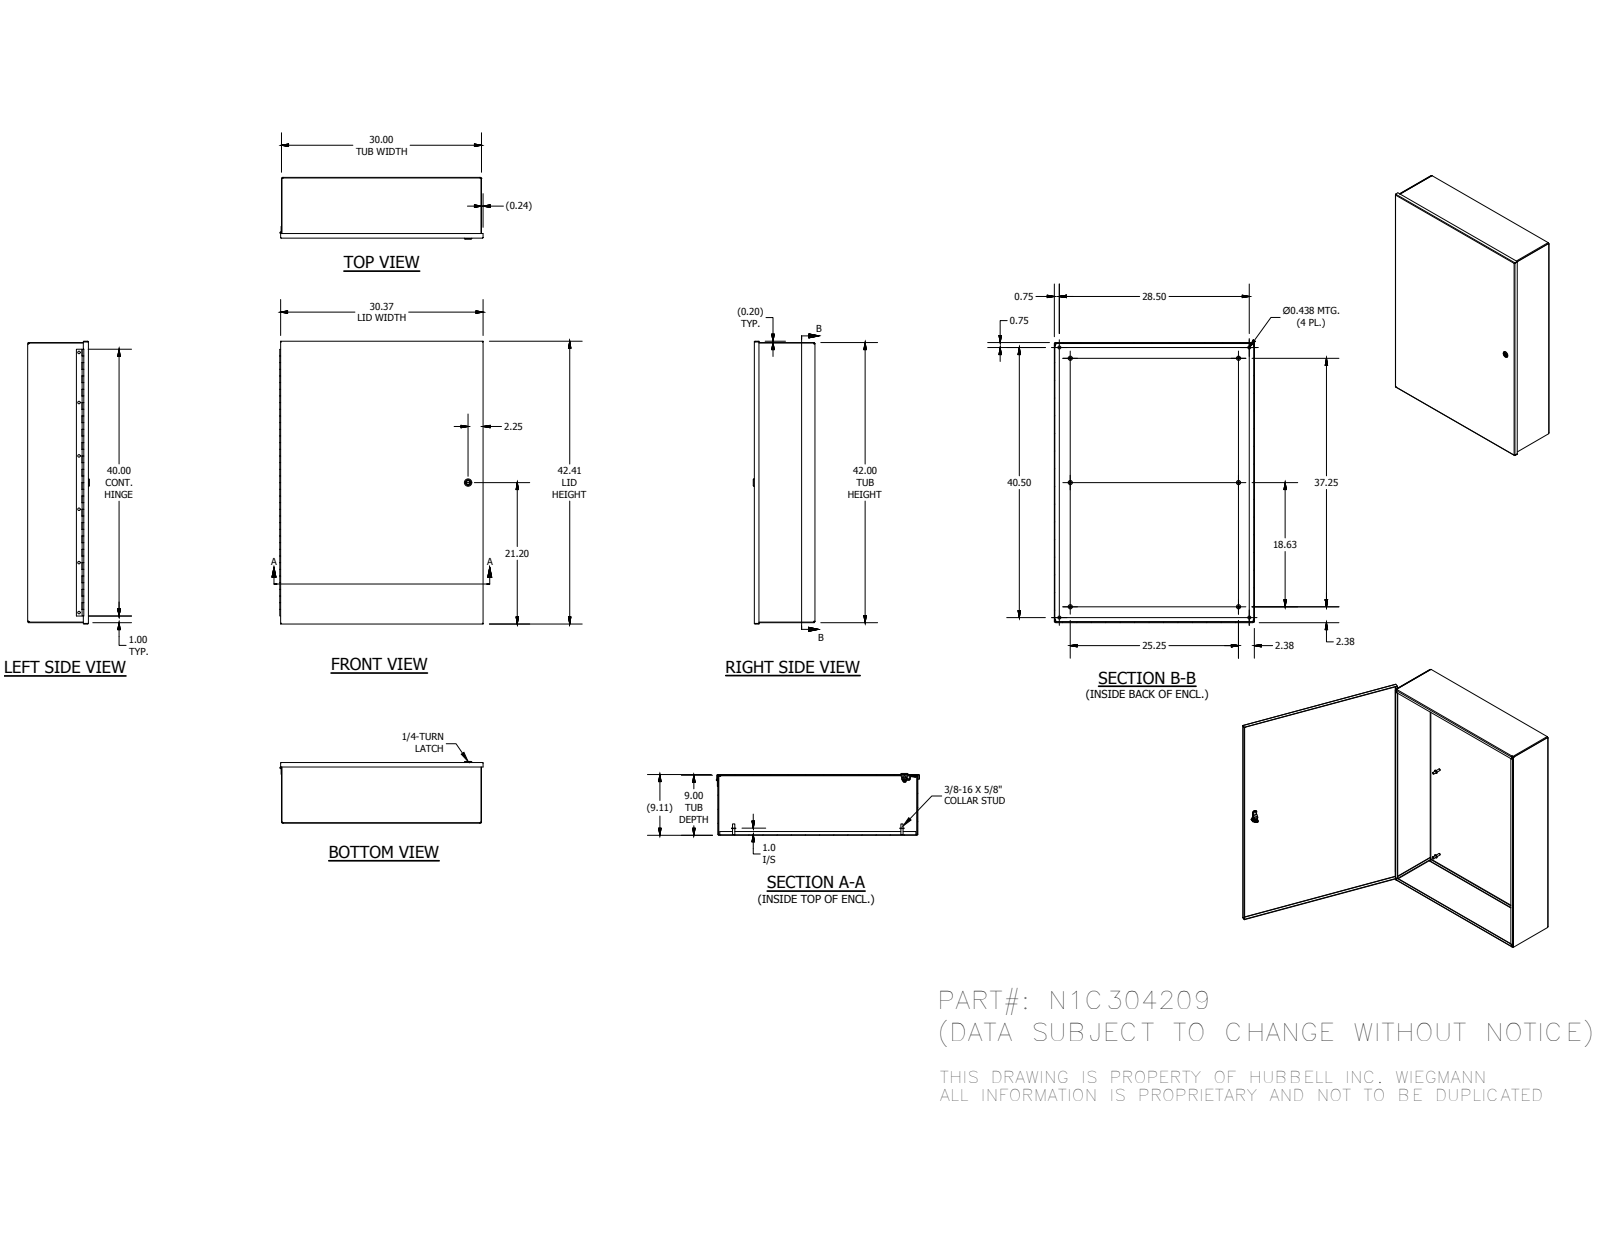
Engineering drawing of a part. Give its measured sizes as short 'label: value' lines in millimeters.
name: N1C304209BLR; N1C3009TB; N1C3042LID; 1000-101-GPF_GPD (+8 more)
written by: Autodesk Inventor 2016 (AUTOMOTIVE_DESIGN)
unit: mm
bodies: 20 solids, 978 faces (637 planar, 273 cylindrical, 68 other)
size: 1077.12 × 774.41 × 235.27
volume: 4 974 000 mm³; area: 5 333 000 mm²
holes: 6× ⌀9.52, 4× ⌀11.11, 1× ⌀3.17, 1× ⌀5, 1× ⌀8, 1× ⌀10, 1× ⌀10.2, 1× ⌀16.1, 1× ⌀20.38
bosses: 6× ⌀15.88, 6× ⌀8.38, 1× ⌀28, 1× ⌀27, 1× ⌀23, 1× ⌀19.8, 1× ⌀15.8, 1× ⌀15.2
rounds: 30× R0.3, 12× R3.47, 10× R0.5, 10× R1.59, 4× R0.79, 4× R2.67, 4× R4, 3× R0.4
face distances: 1.88, 229.39, 227.51, 231.27, 760.12, 1064.92, 758.24, 762, 1063.04, 1066.8
hole spacings: 203.2, 190.5, 393.7, 406.4, 515.35, 596.9, 723.9, 800.1
